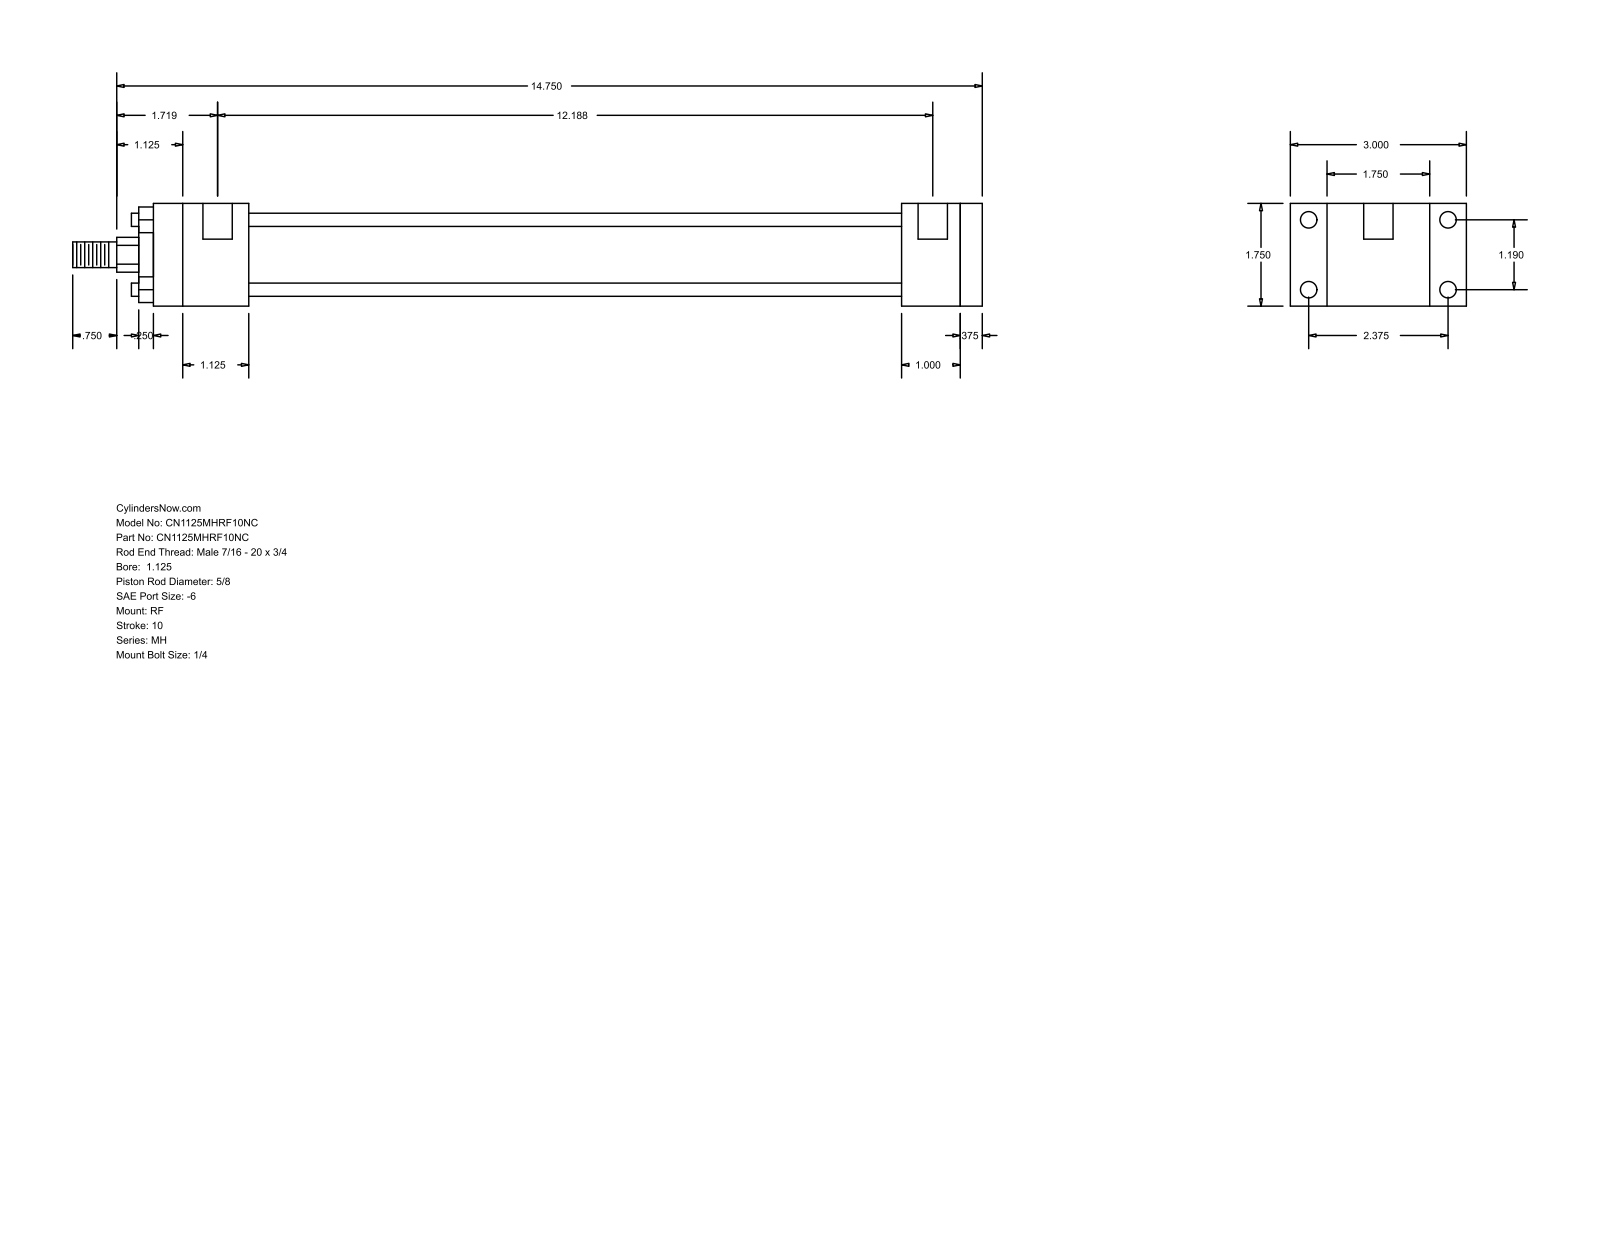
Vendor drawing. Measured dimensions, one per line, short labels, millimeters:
name: MH_RF__0112_0.625
written by: GSSL Pune (CONFIG_CONTROL_DESIGN)
unit: mm
bodies: 0 solids, 92 faces (64 planar, 28 cylindrical, 0 other)
size: 393.7 × 76.2 × 44.45
holes: 4× ⌀5.56, 4× ⌀7.14, 2× ⌀12.7
bosses: 4× ⌀5.71, 1× ⌀34.92, 1× ⌀28.57, 1× ⌀15.88, 1× ⌀11.11
rounds: 1× R7.54
face distances: 44.46, 9.53, 358.77, 15.87, 307.97, 317.5, 282.58, 25.39, 34.92, 41.27
hole spacings: 30.22, 60.32, 67.47, 306.39, 3.17, 309.56
